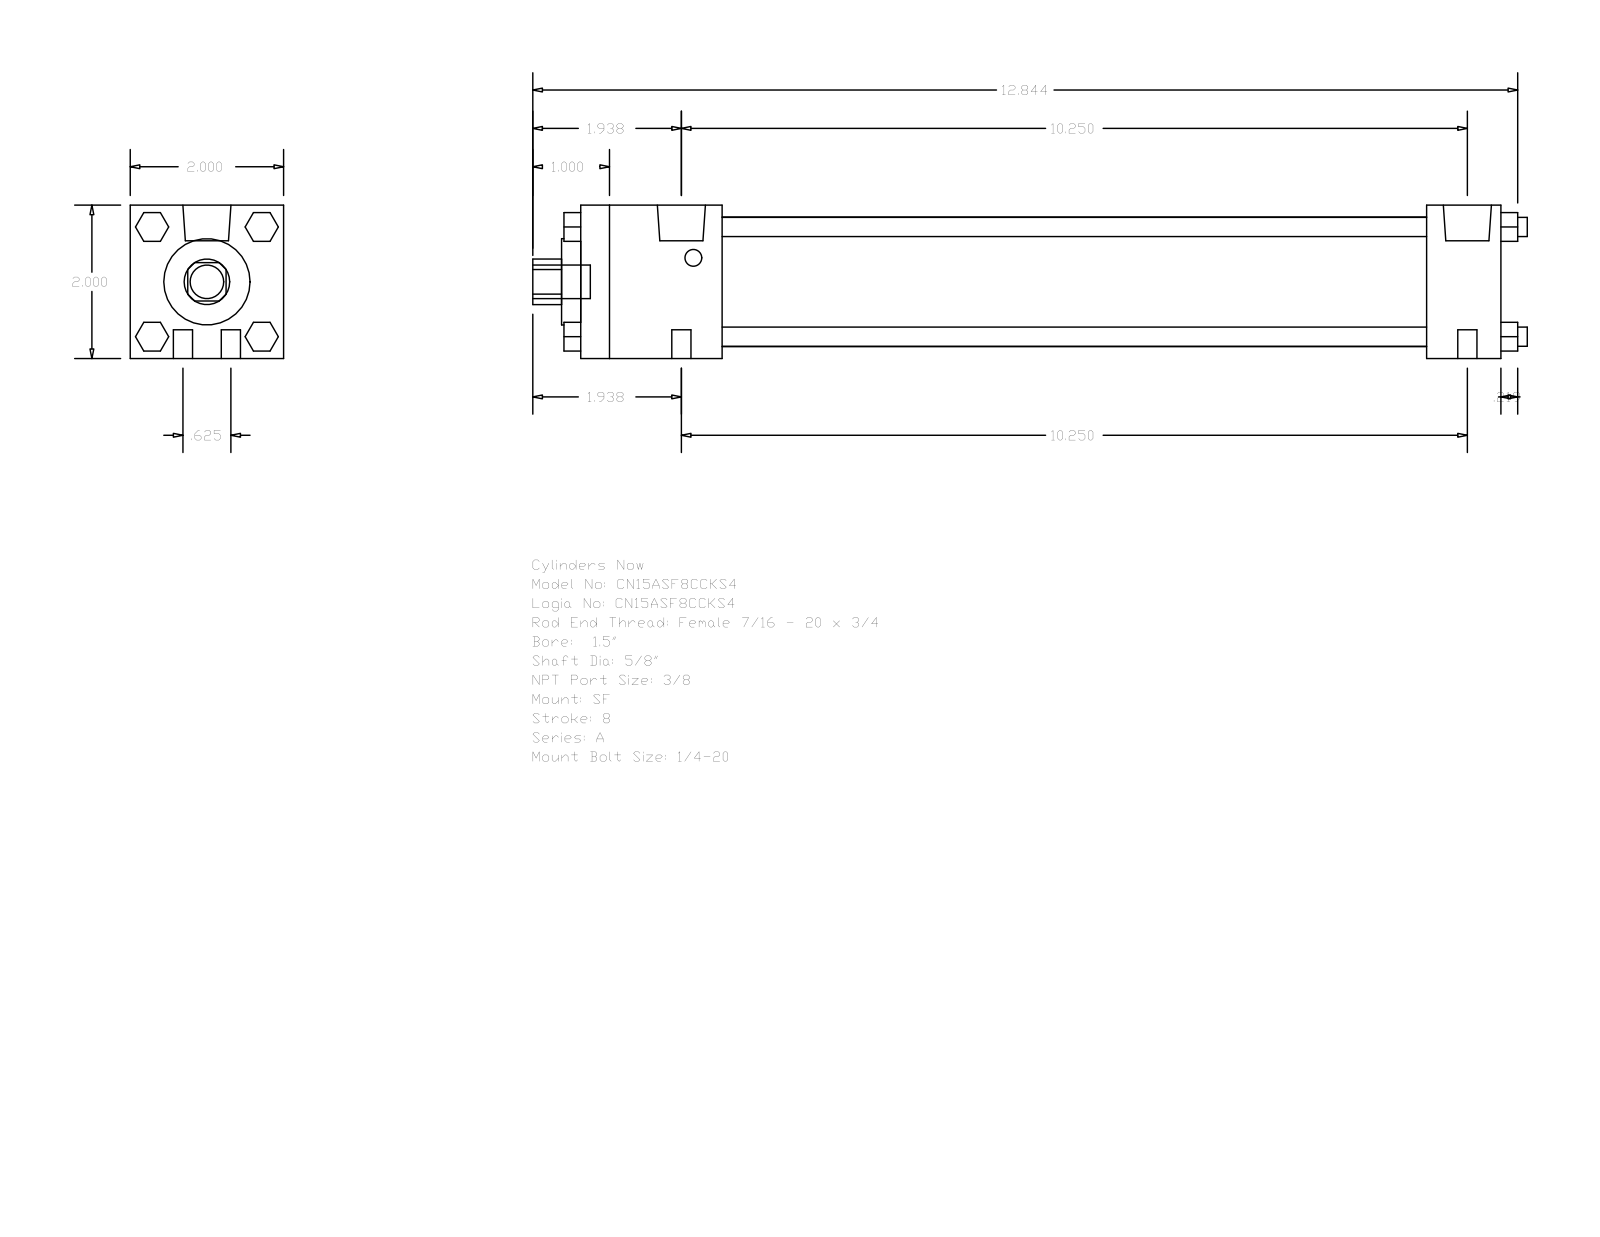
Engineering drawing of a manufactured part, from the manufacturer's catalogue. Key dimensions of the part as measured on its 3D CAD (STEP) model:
Part name (STEP PRODUCT): A_SF__0150_0.625
STEP written by: GSSL Pune (CONFIG_CONTROL_DESIGN)
Units: millimetres
Bodies: 0 solids, 124 faces (94 planar, 30 cylindrical, 0 other)
Overall size (bounding box): 329.41 × 50.8 × 50.8
Round holes (diameter × count): ⌀15.88 ×1, ⌀28.57 ×1, ⌀42.93 ×1
Round bosses / shafts (diameter × count): ⌀6.35 ×8, ⌀15.93 ×2, ⌀5.56 ×2, ⌀11.11 ×1
Partial cylindrical surfaces — rounded edges, fillets, slot ends (radius × count): R7.54 ×1
Main face-to-face distances: 50.8, 304.8, 46.83, 280.19, 233.36, 257.97, 24.61, 9.52, 6.35, 53.18
